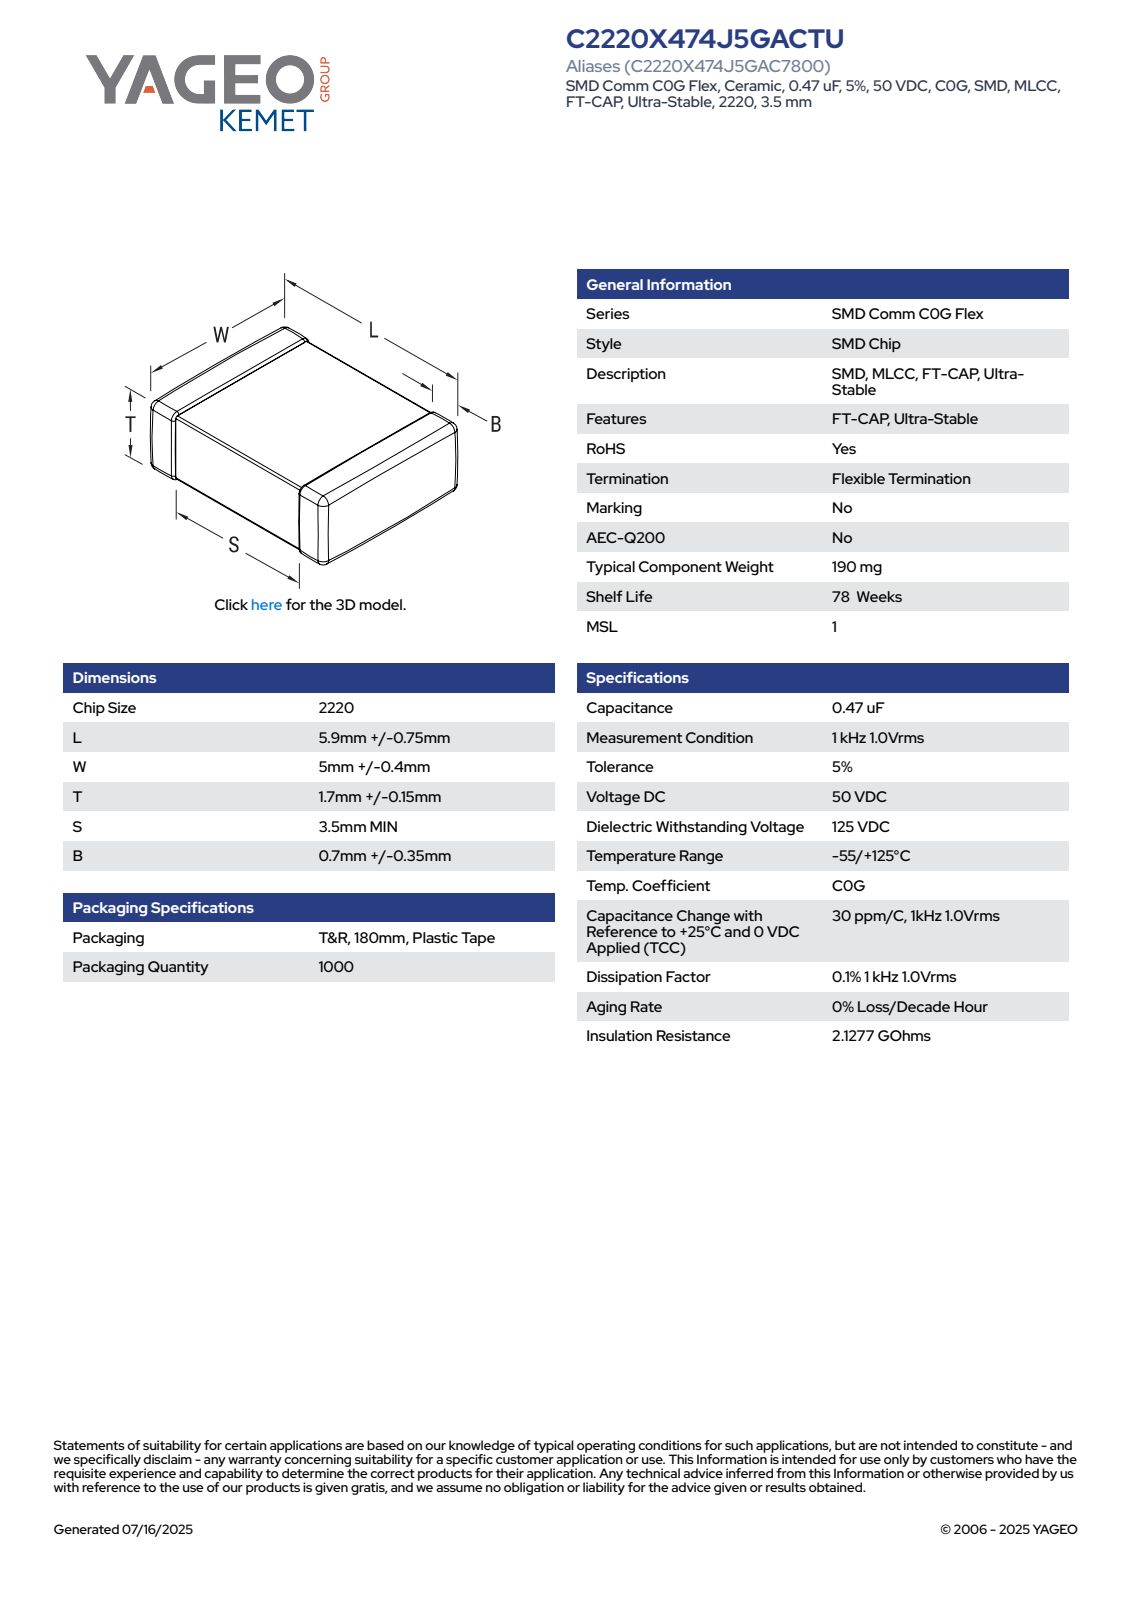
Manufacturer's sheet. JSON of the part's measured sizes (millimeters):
{"part_name": "CCS_CCSTDNOS_2220_L6.65W5.4T1.85B1.05", "step_written_by": "SolidWorks 2014 (AUTOMOTIVE_DESIGN)", "units": "millimeters", "bodies": {"solids": 4, "faces": 121, "planar": 71, "cylindrical": 34, "other": 16}, "overall_size": [6.65, 5.4, 1.85], "volume_mm3": 59, "surface_area_mm2": 113, "partial_cylinders_radius": [[0.11, 24]], "face_to_face_distances": [1.63, 1.74, 1.85, 6.65, 5.18, 5.29, 5.4, 2.51, 2.78, 2.62]}
